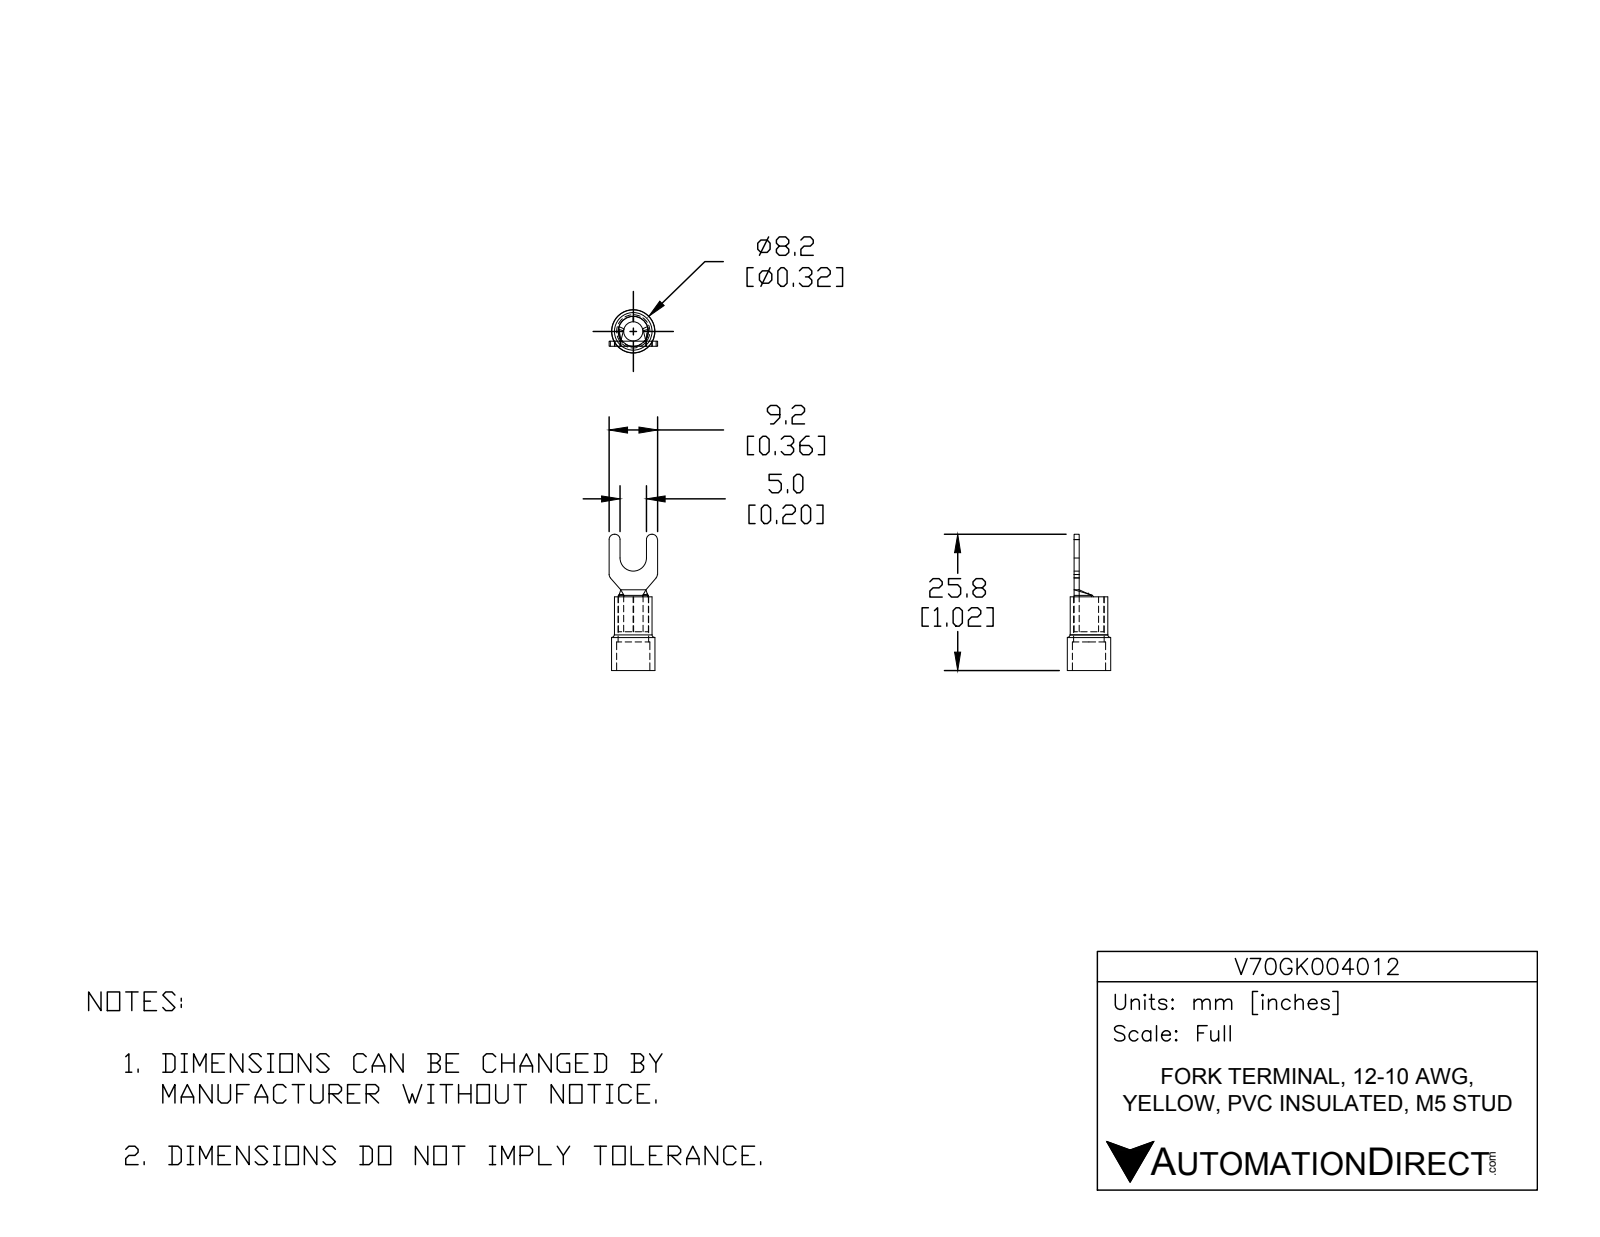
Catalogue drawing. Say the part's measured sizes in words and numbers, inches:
The part is named "V70GK004012". Its 3-D file was written by "SolidWorks 2017 (AUTOMOTIVE_DESIGN)". It is 2 solids with 48 faces: 19 planar, 21 cylindrical and 8 other. Overall it measures 1.016 by 0.36 by 0.323 inches. Its volume is 0.025 cubic inches and its surface area 1.628 square inches. Round holes: 1 of diameter 0.144, 1 of diameter 0.227, 1 of diameter 0.248. Round bosses or shafts: 1 of diameter 0.323, 1 of diameter 0.28, 1 of diameter 0.223. Partial cylindrical surfaces (rounded edges, fillets, slot ends): 6 of radius 0.039, 1 of radius 0.098. The main face-to-face distances are 0.039, 0.55, 0.29, 0.26, 0.096, 0.1, 0.36, 0.178, 0.182, 0.182.
